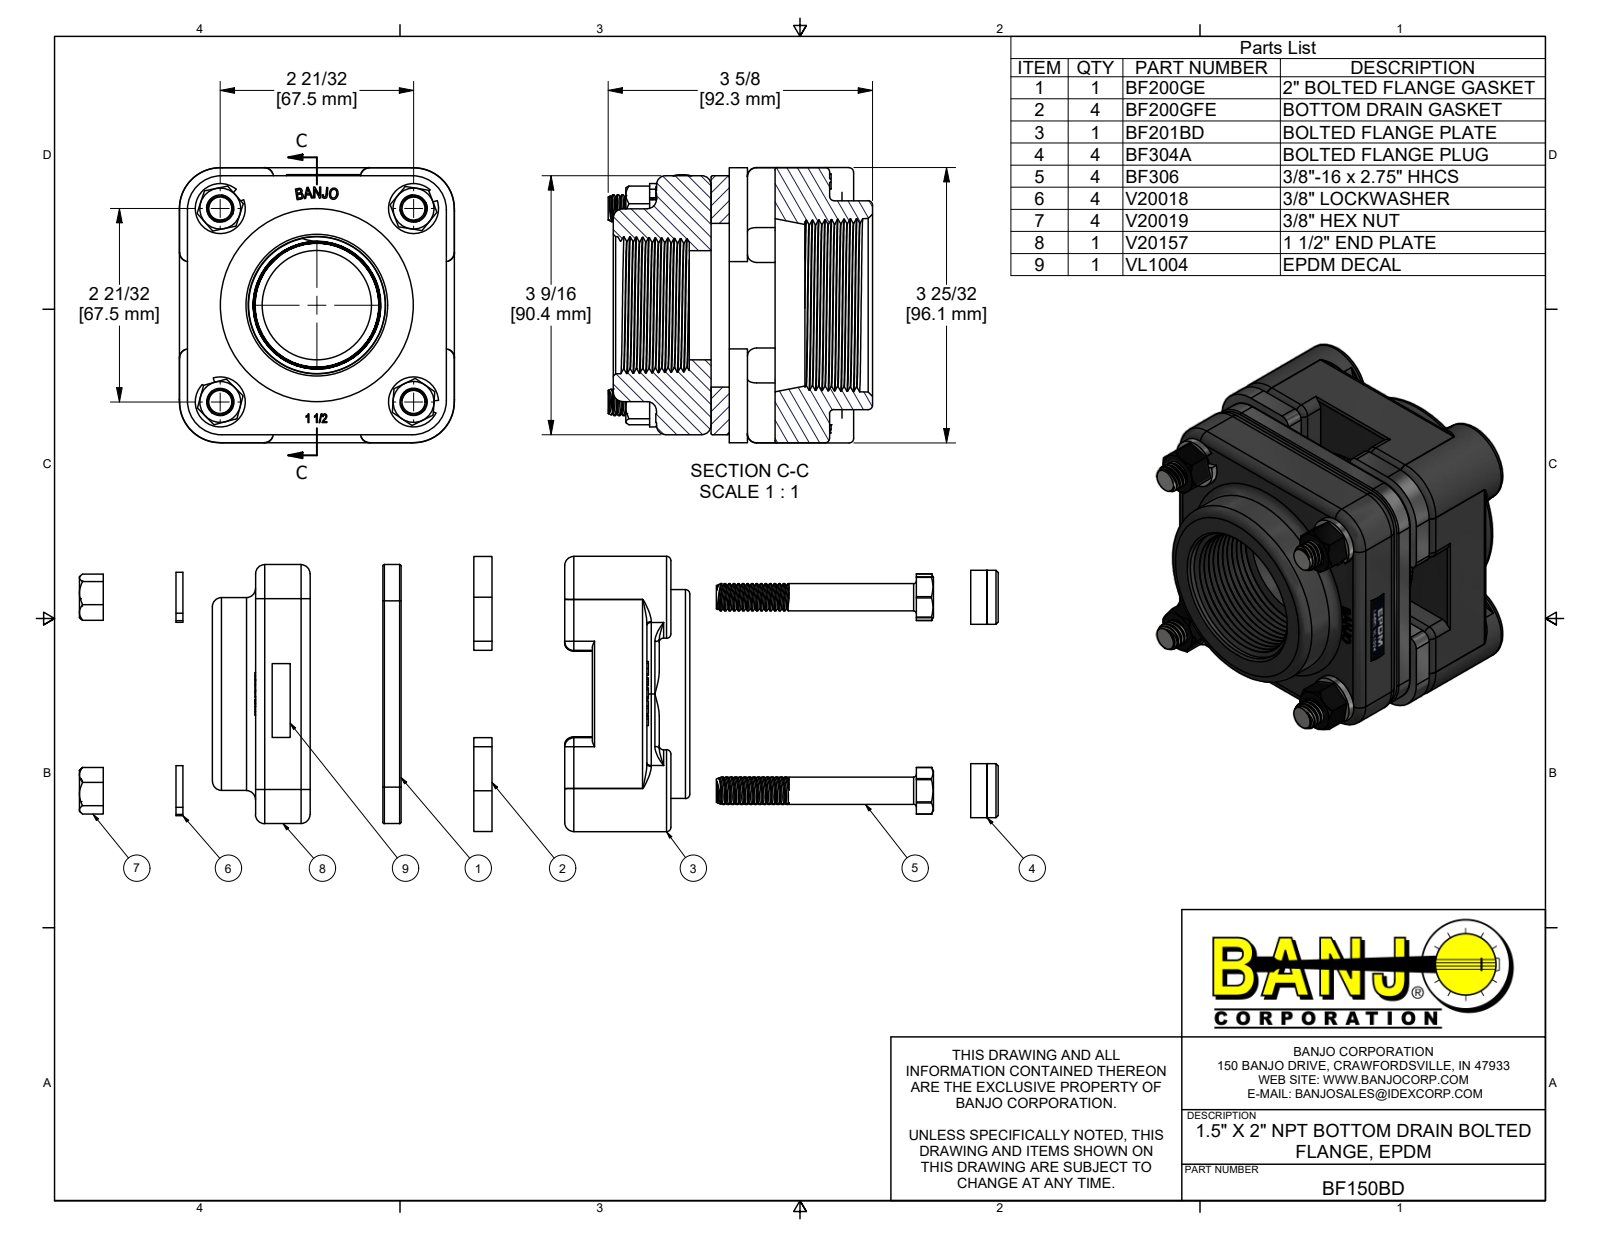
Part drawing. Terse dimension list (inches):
name: BF150BD; BF200GE; V20157; V20019 (+6 more)
written by: Autodesk Inventor 2019 (AUTOMOTIVE_DESIGN)
unit: in
bodies: 24 solids, 1342 faces (423 planar, 403 cylindrical, 516 other)
size: 30.446 × 3.784 × 3.784
volume: 25.63 in³; area: 363.7 in²
holes: 4× ⌀0.307, 4× ⌀0.38, 4× ⌀0.385, 4× ⌀0.406, 4× ⌀0.41, 4× ⌀0.422, 4× ⌀0.715, 4× ⌀0.75, 1× ⌀1.5, 1× ⌀2.25
bosses: 60× ⌀0.324, 4× ⌀1.125, 4× ⌀0.742, 4× ⌀0.687, 4× ⌀0.375, 1× ⌀2.87, 1× ⌀2.65
rounds: 48× R0.125, 16× R0.02, 12× R0.06, 8× R0.162, 5× R1.19, 4× R0.03, 4× R0.32, 4× R0.469
face distances: 0.25, 0.5, 0.111, 3.671, 0.75, 1.63, 1, 1.25, 3.782, 3.56
hole spacings: 1.88, 2.659, 3.761
